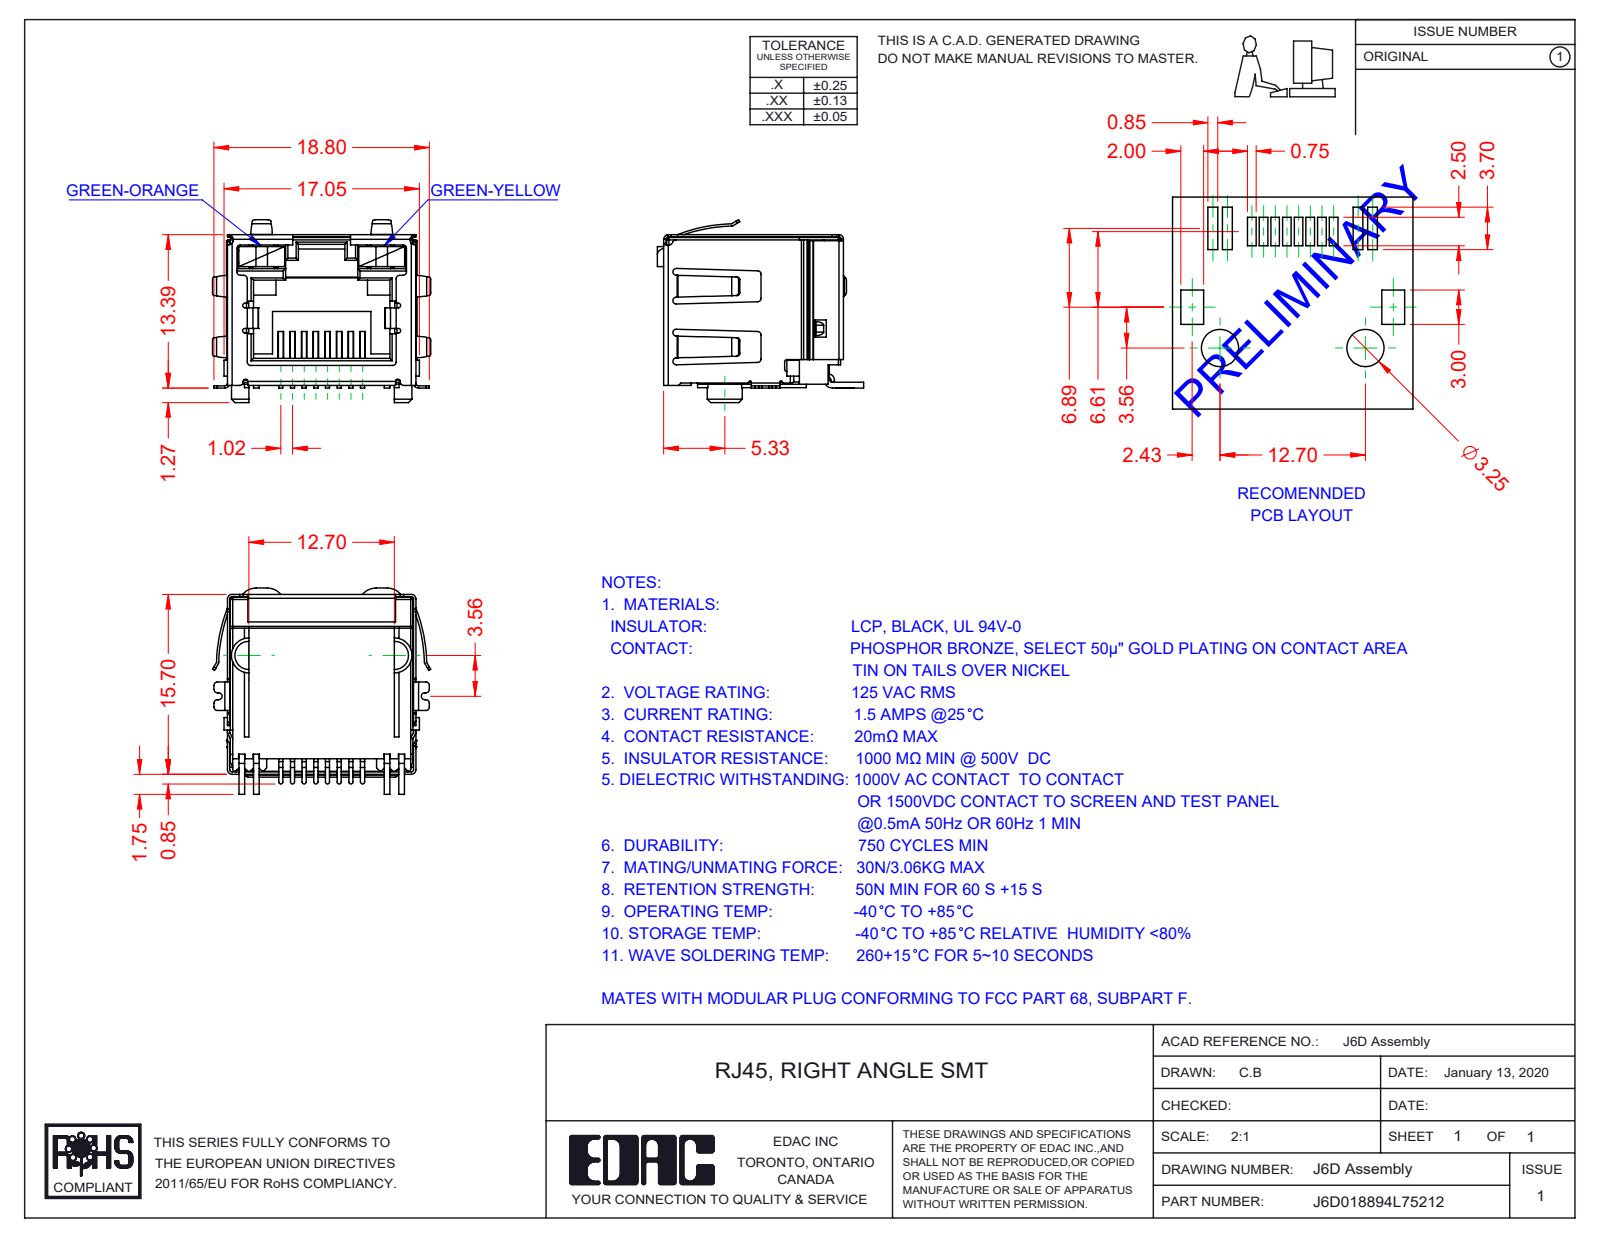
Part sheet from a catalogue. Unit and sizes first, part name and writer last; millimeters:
Units: millimetres
Overall size (bounding box): 19.06 × 18 × 15.95
Partial cylindrical surfaces — rounded edges, fillets, slot ends (radius × count): R0.3 ×55, R0.2 ×40, R0.4 ×19, R0.25 ×16, R0.1 ×12, R0.15 ×8, R0.18 ×8, R0.5 ×6
Main face-to-face distances: 16, 16.2, 16.25, 2.25, 1, 15.95, 12.8, 0.45, 13.05, 10.6
Volume: 1 790 mm³ · Surface area: 4 796 mm²
Bodies: 12 solids, 1034 faces (703 planar, 286 cylindrical, 45 other)
Part name (STEP PRODUCT): 6D LED LH_7-Green-Orange; 6D LED RH_5-Green-Yellow; 6D Insulator; 6D Contacts (+2 more)
STEP written by: SolidWorks 2016 (CONFIG_CONTROL_DESIGN)
